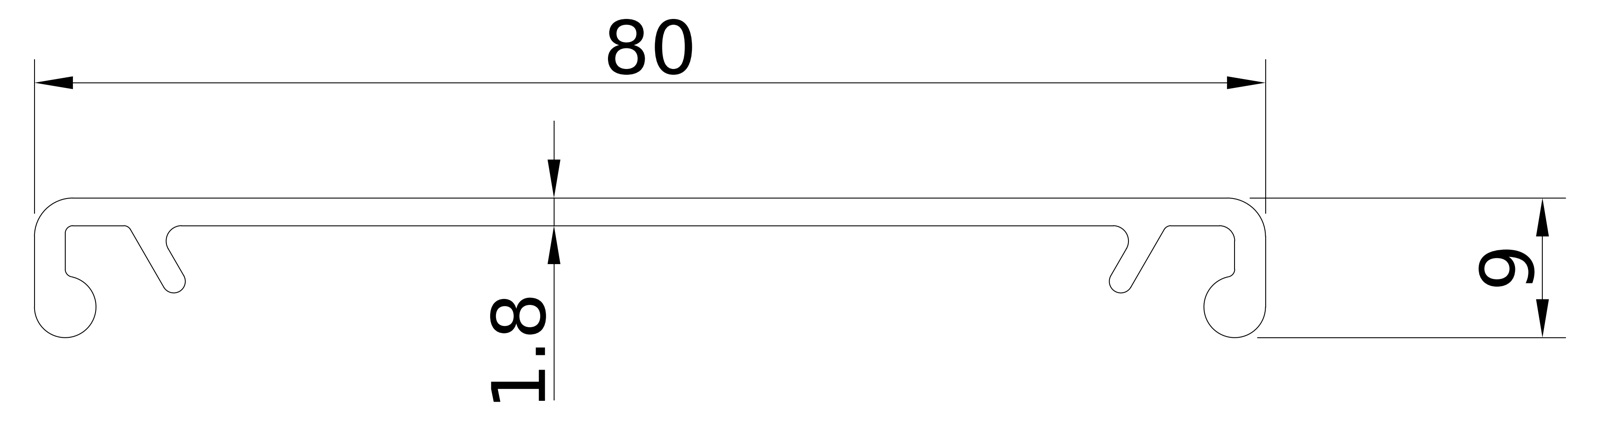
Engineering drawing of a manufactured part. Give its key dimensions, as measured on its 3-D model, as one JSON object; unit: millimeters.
{"part_name": "BPRCA0000017", "step_written_by": "Autodesk Inventor 2022 (AUTOMOTIVE_DESIGN)", "units": "millimeters", "bodies": {"solids": 1, "faces": 28, "planar": 14, "cylindrical": 14, "other": 0}, "overall_size": [100, 80, 9.08], "volume_mm3": 19737, "surface_area_mm2": 21155, "partial_cylinders_radius": [[0.5, 5], [1, 3], [0.75, 2], [2, 2], [2.5, 2]], "face_to_face_distances": [1.8, 80, 2, 78, 1.5, 100, 76]}
